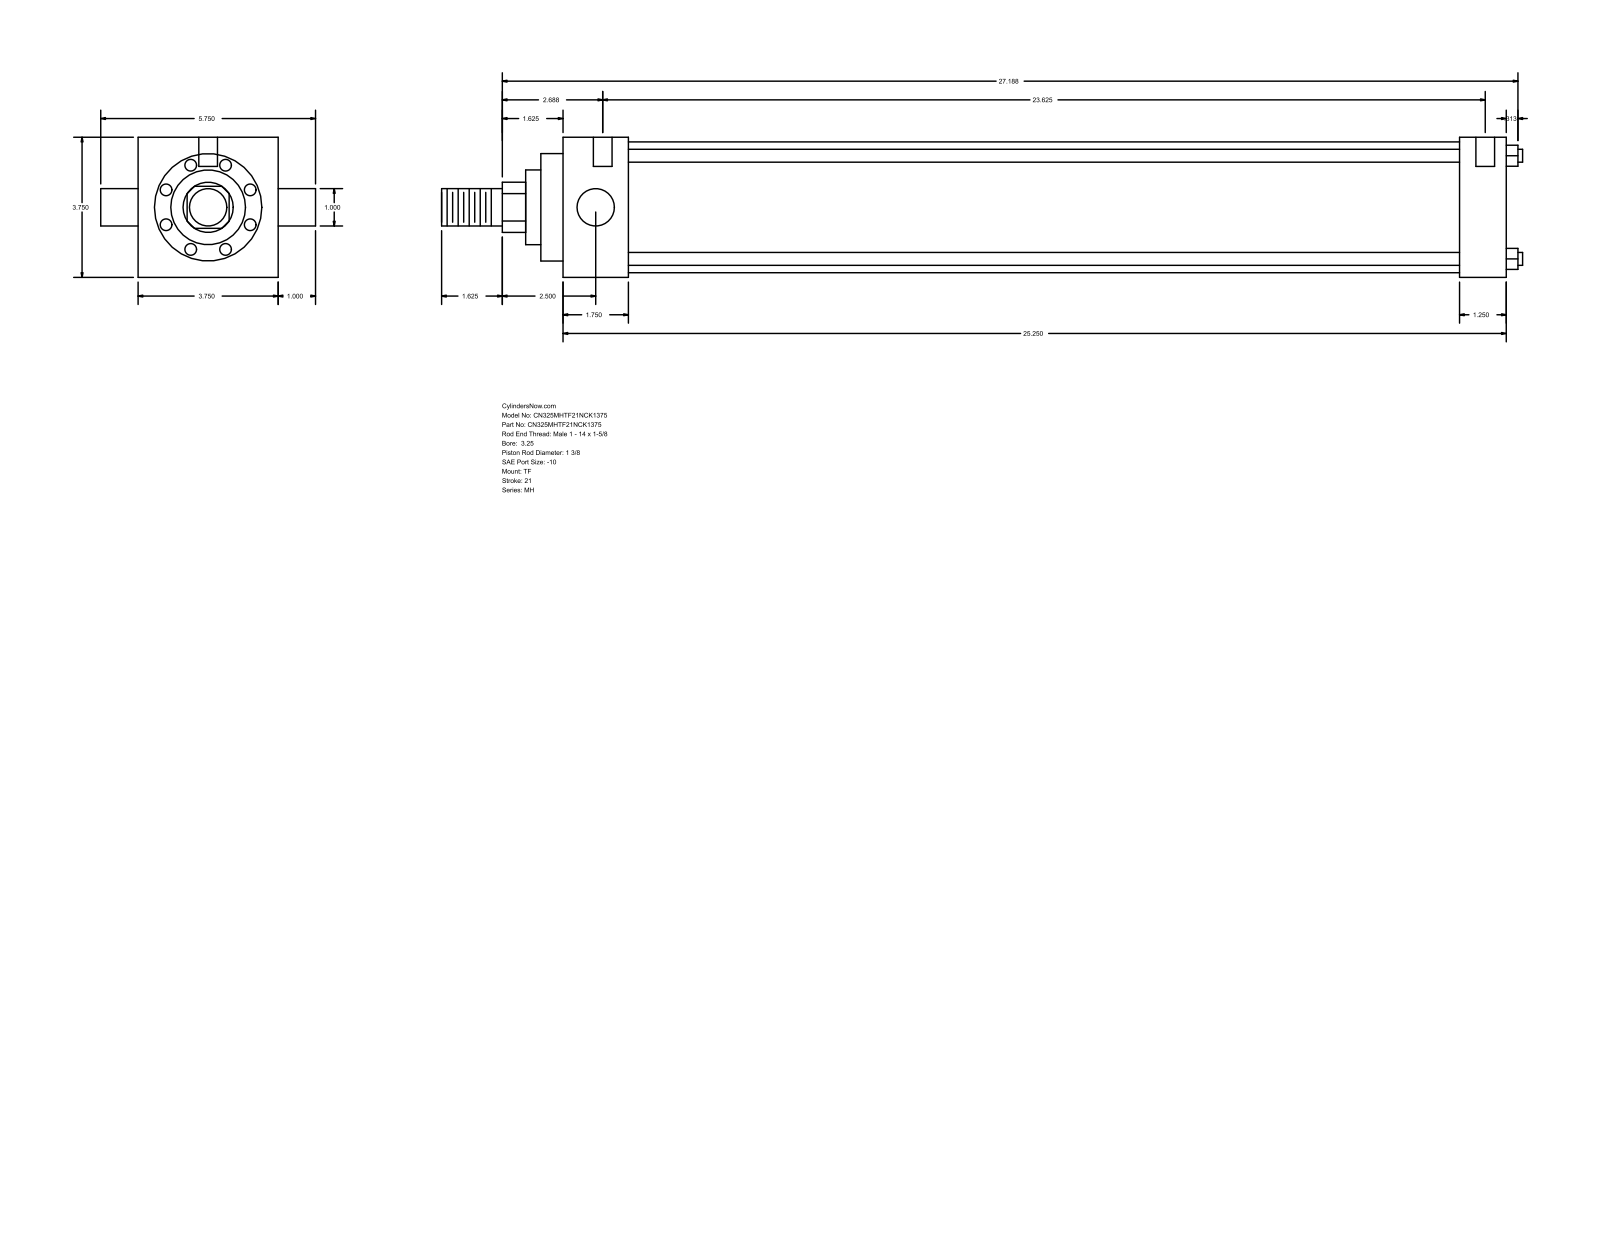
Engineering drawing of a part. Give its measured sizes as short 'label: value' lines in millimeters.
name: MH_TF__0325_1.375
written by: GSSL Pune (CONFIG_CONTROL_DESIGN)
unit: mm
bodies: 0 solids, 86 faces (61 planar, 25 cylindrical, 0 other)
size: 735.01 × 146.05 × 95.25
holes: 3× ⌀5.56, 2× ⌀12.7
bosses: 4× ⌀8.76, 2× ⌀25.4, 1× ⌀88.9, 1× ⌀73.03, 1× ⌀50.8, 1× ⌀34.92
rounds: 1× R17.06
face distances: 95.24, 641.35, 44.45, 609.61, 565.16, 596.9, 31.74, 15.08, 59.53, 624.69
hole spacings: 1.59, 4.76, 600.08, 601.67, 604.84, 606.43
